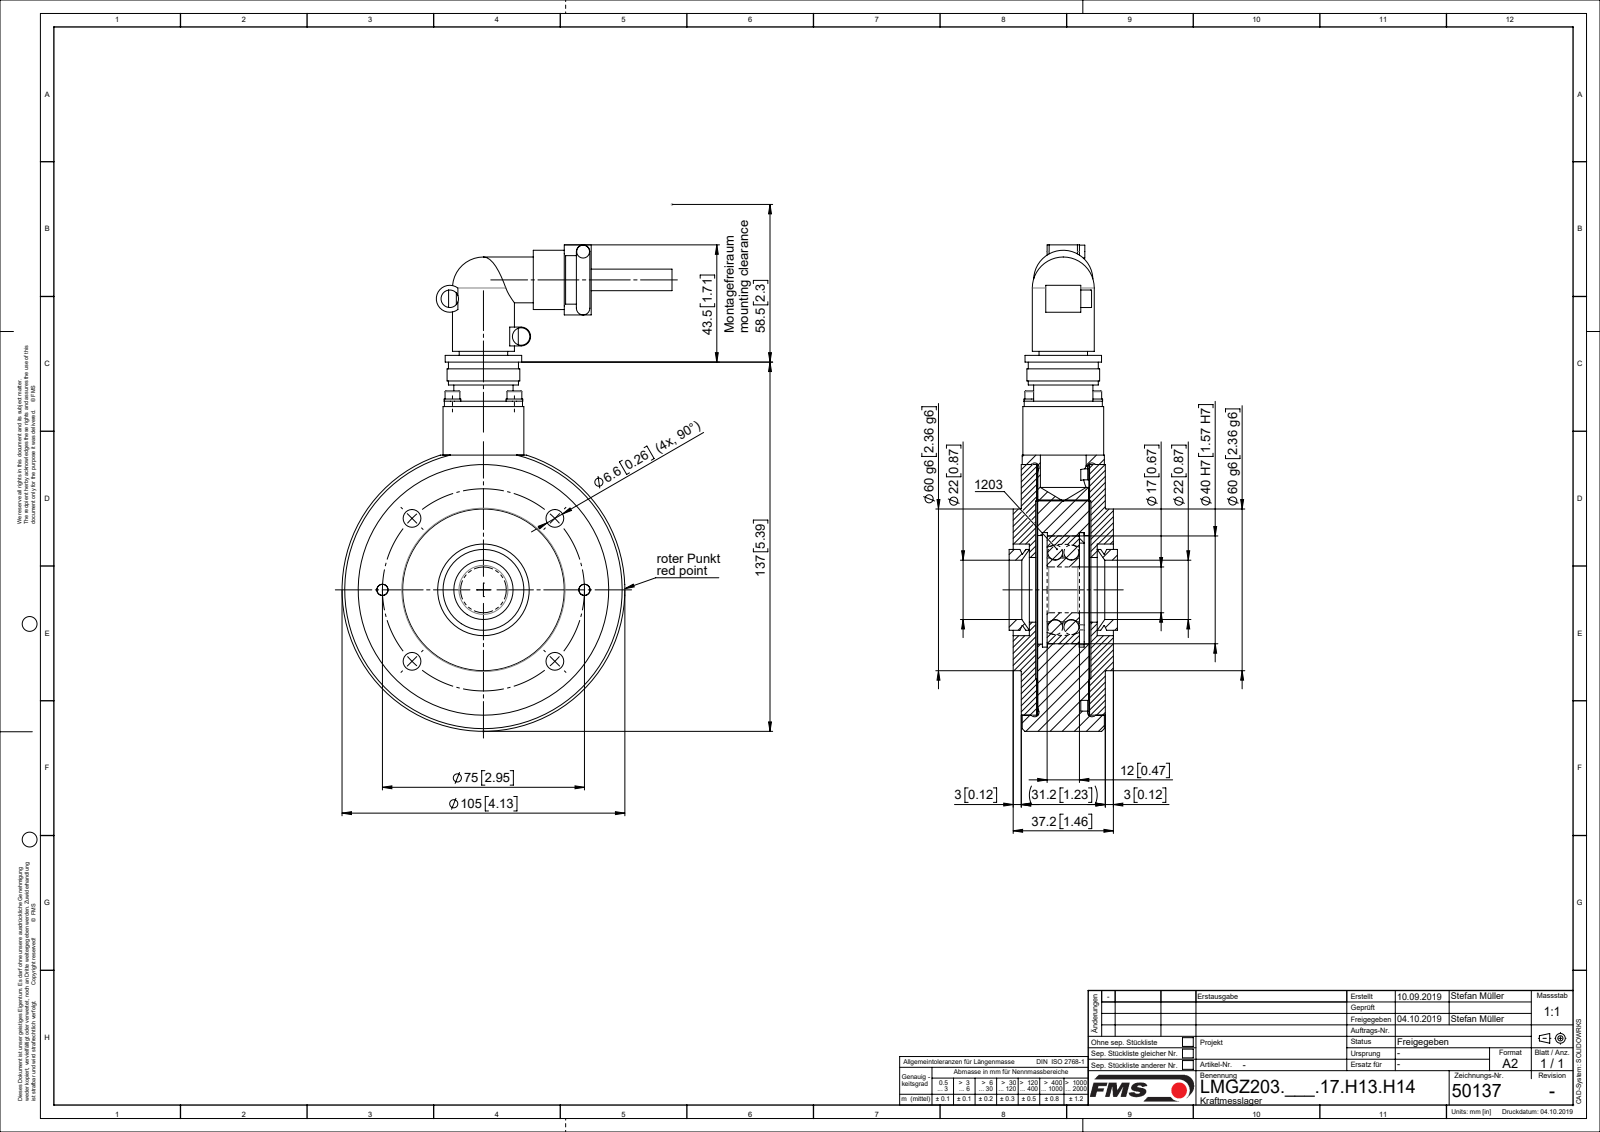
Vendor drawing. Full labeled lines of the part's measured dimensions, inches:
Part name (STEP PRODUCT): ZEICHNUNG7; L50137; L4795904; L47958(1) (+8 more)
STEP written by: Mechanical Desktop 2007 (CONFIG_CONTROL_DESIGN)
Units: inches
Bodies: 21 solids, 407 faces (125 planar, 231 cylindrical, 51 other)
Overall size (bounding box): 7.106 × 4.823 × 1.465
Volume: 18.16 in³ · Surface area: 165.5 in²
Round holes (diameter × count): ⌀0.102 ×4, ⌀0.126 ×4, ⌀0.134 ×4, ⌀0.138 ×4, ⌀0.26 ×4, ⌀0.157 ×2, ⌀0.209 ×2, ⌀0.217 ×2, ⌀0.394 ×2, ⌀0.669 ×1, ⌀0.866 ×1, ⌀0.906 ×1
Round bosses / shafts (diameter × count): ⌀0.244 ×4, ⌀0.217 ×4, ⌀0.118 ×4, ⌀0.315 ×3, ⌀0.866 ×2, ⌀0.256 ×2, ⌀0.197 ×2, ⌀0.189 ×2
Partial cylindrical surfaces — rounded edges, fillets, slot ends (radius × count): R0.098 ×2, R0.079 ×1, R0.138 ×1, R0.197 ×1
Main face-to-face distances: 0.758, 0.748, 0.23, 0.24, 0.988, 0.998, 0.787, 0.768, 0.02, 0.778
Hole centre spacings: 1.476, 0.64, 0.906, 1.13, 2.088, 2.728, 1.281, 2.953
